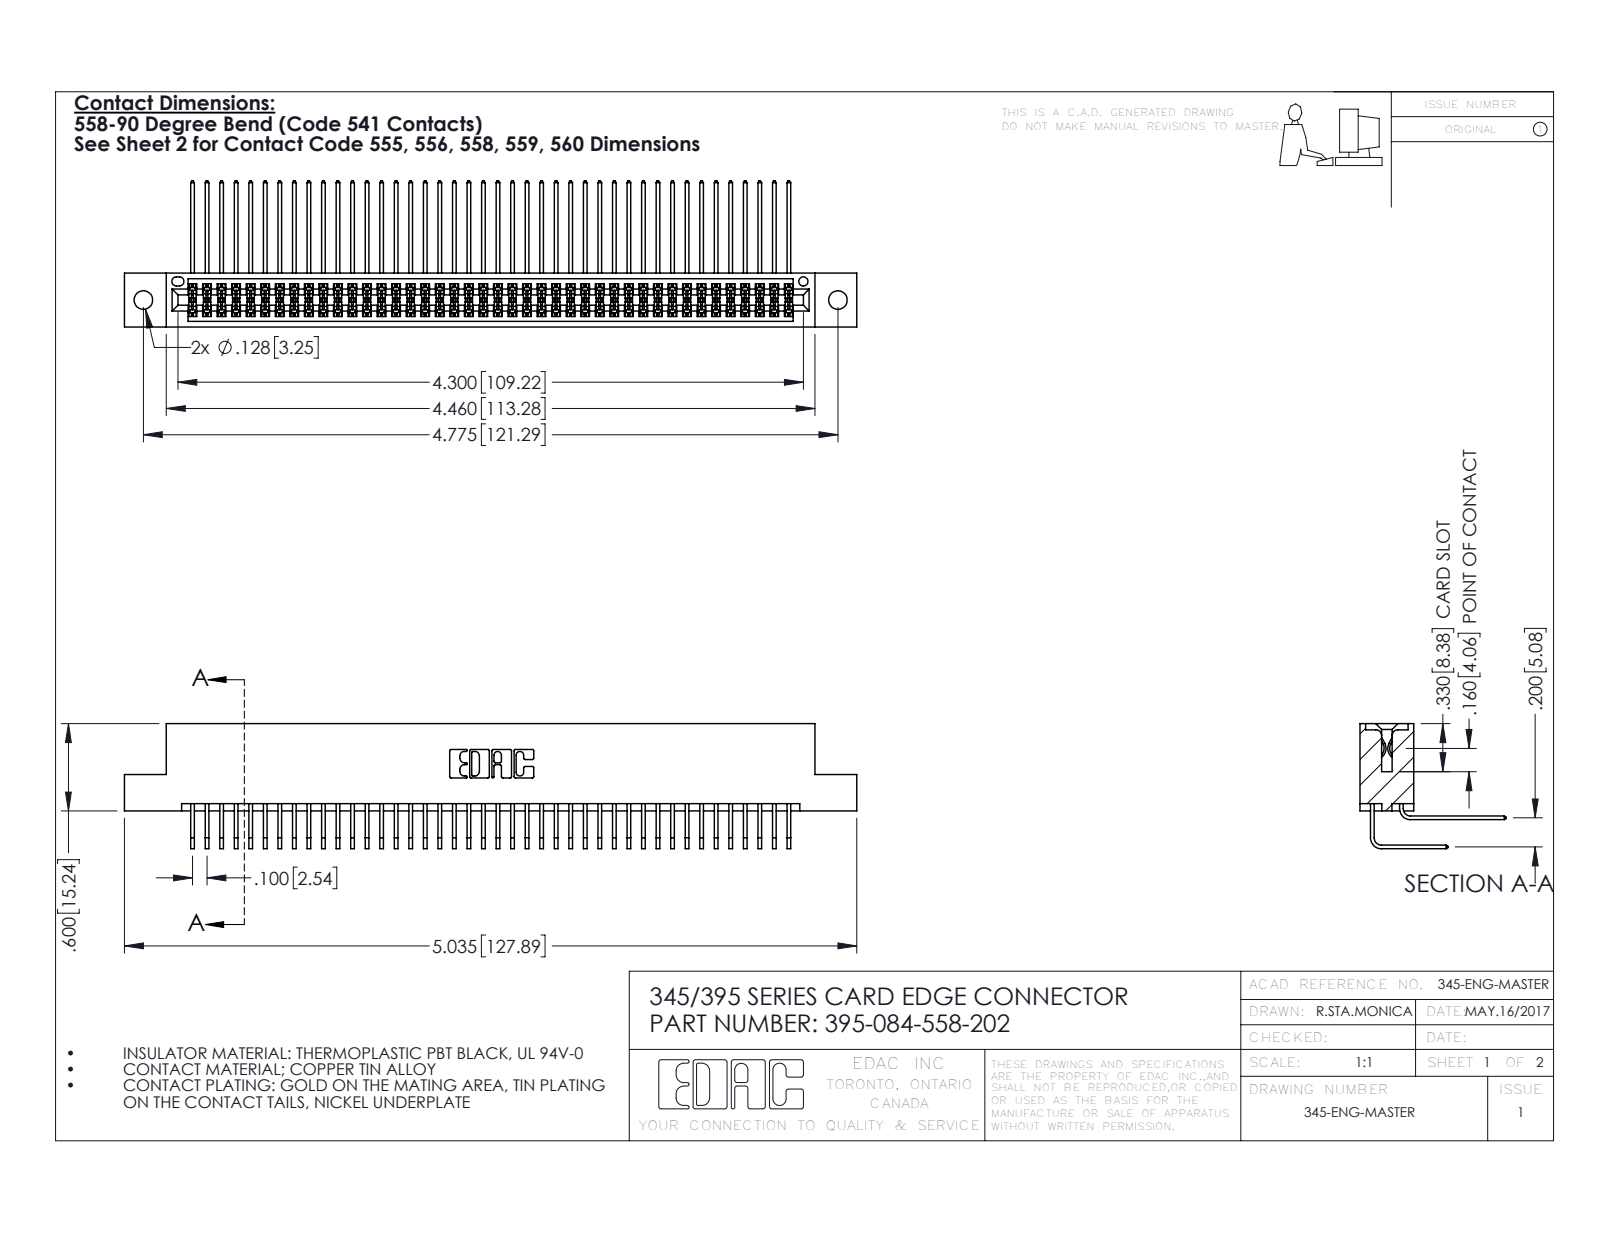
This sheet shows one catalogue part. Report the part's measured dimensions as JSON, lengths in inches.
{"part_name": "345-292-001_558 Tail - 2; 345 Part_Flush Mounting Lugs - 0.128 Dia; 395-084-558-202; 345-292-001_558 559 Tail - 1", "step_written_by": "SolidWorks 2016 (CONFIG_CONTROL_DESIGN)", "units": "inches", "bodies": {"solids": 85, "faces": 4494, "planar": 3020, "cylindrical": 1474, "other": 0}, "overall_size": [5.035, 1.005, 0.859], "volume_in3": 0.785, "surface_area_in2": 32.6, "round_holes": [[0.128, 2], [0.064, 1]], "partial_cylinders_radius": [[0.006, 127], [0.01, 22], [0.007, 6], [0.031, 6], [0.026, 3], [0.014, 2], [0.019, 2], [0.022, 2]], "face_to_face_distances": [0.072, 0.298, 0.2, 0.37, 0.098, 0.272, 0.025, 0.225, 0.025, 0.175], "hole_center_spacings": [0.27, 4.539, 4.775]}
